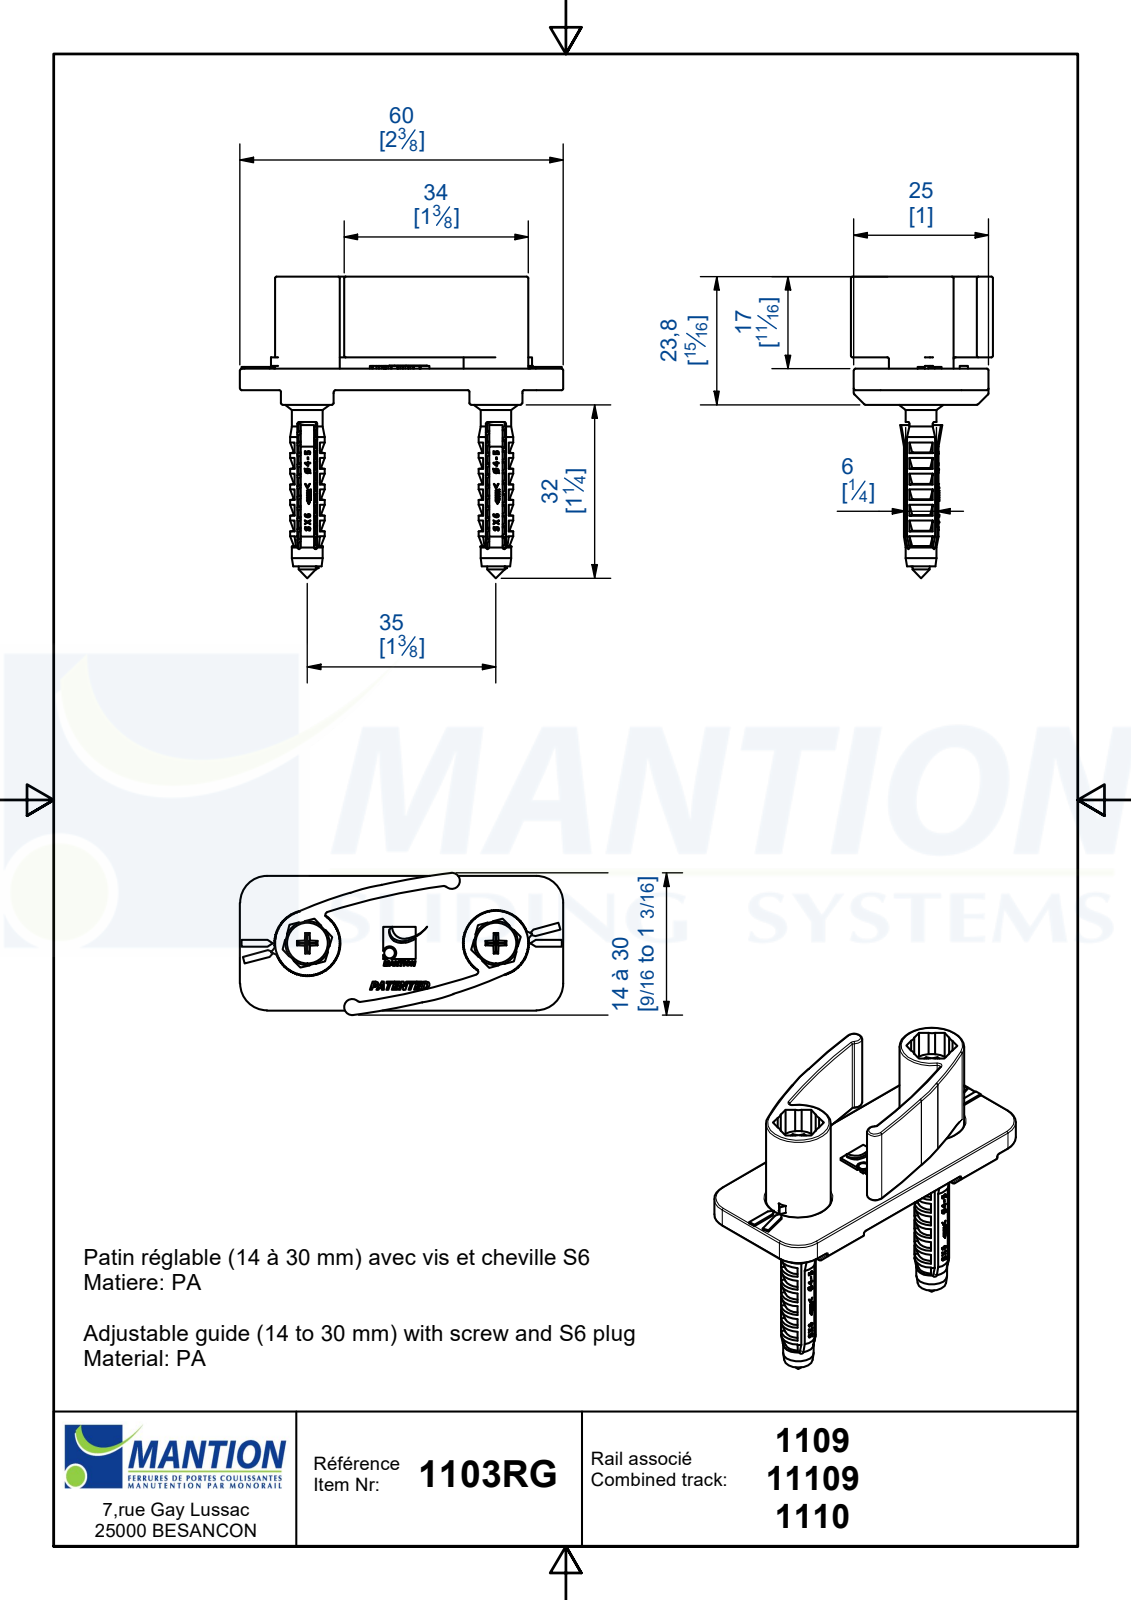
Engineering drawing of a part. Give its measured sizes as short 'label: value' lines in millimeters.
name: 1103RG; 21267-1A; vis TR 4.2x50; C0002420 - CHEVILLE UNIVERSELLE 6 X 30 (+1 more)
written by: Autodesk Inventor 2019 (AUTOMOTIVE_DESIGN)
unit: mm
bodies: 7 solids, 1829 faces (1281 planar, 211 cylindrical, 337 other)
size: 60 × 56 × 26.38
volume: 13 324 mm³; area: 12 834 mm²
holes: 2× ⌀3.67, 2× ⌀5.1, 2× ⌀8.5, 2× ⌀12.2, 1× ⌀2.42
bosses: 2× ⌀12, 2× ⌀6.4, 2× ⌀5.7, 2× ⌀3.2, 1× ⌀1.94
rounds: 44× R0.3, 12× R2, 8× R0.25, 8× R0.5, 6× R0.1, 4× R5, 2× R1.5, 2× R2.11
face distances: 4, 2.7, 35, 6.7, 0.6, 3.1, 3.65, 3.05, 6.15, 6.75
hole spacings: 15.36, 19.83, 35
